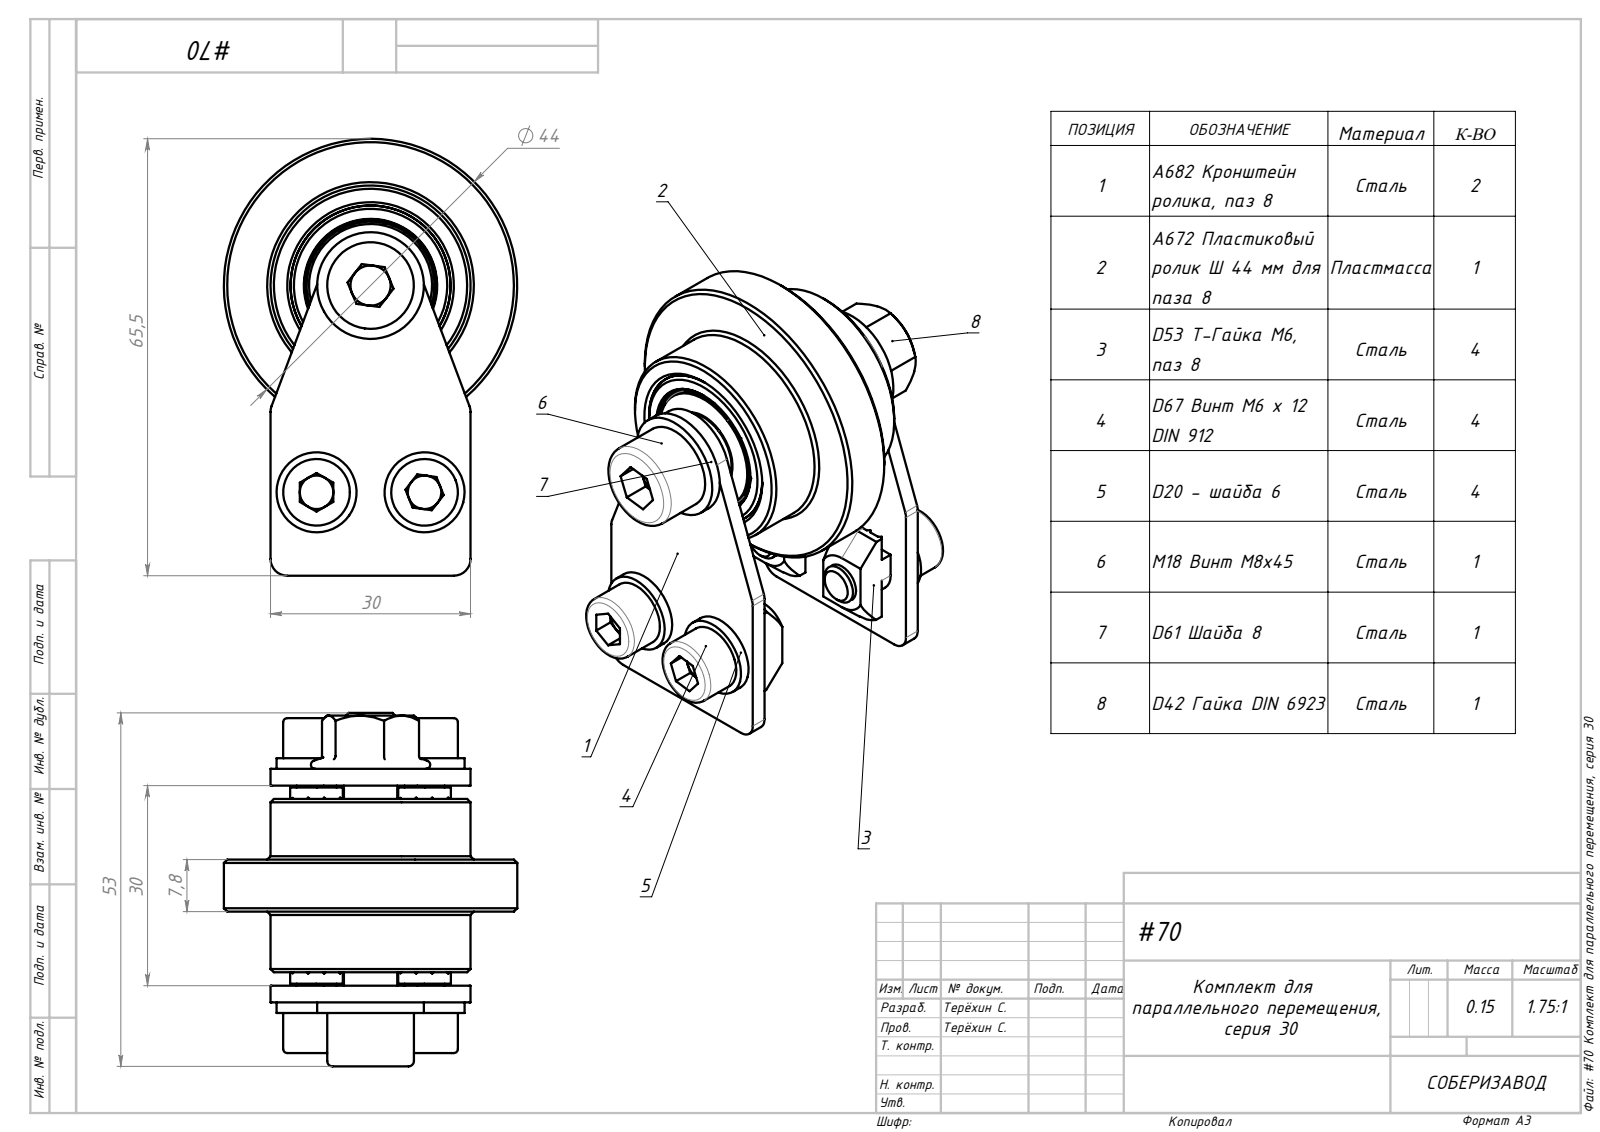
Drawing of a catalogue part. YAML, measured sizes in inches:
part_name: "Набор ролика, 30 серия; D61 Шайба 8_00; D53 Т-Гайка М6, паз 8_00; A682 Кронштейн ролика, паз 8_00 (+5 more)"
step_written_by: "SolidWorks 2022 (AUTOMOTIVE_DESIGN)"
units: inches
bodies: {solids: 24, faces: 655, planar: 397, cylindrical: 126, other: 132}
overall_size: [2.579, 2.087, 1.732]
volume: 2.181
surface_area: 42.48
round_holes:
  - {diameter: 0.197, count: 2}
  - {diameter: 0.244, count: 2}
  - {diameter: 0.252, count: 2}
  - {diameter: 0.268, count: 1}
  - {diameter: 0.315, count: 1}
  - {diameter: 0.323, count: 1}
  - {diameter: 0.331, count: 1}
  - {diameter: 0.48, count: 1}
  - {diameter: 0.787, count: 1}
  - {diameter: 0.945, count: 1}
round_bosses_or_shafts:
  - {diameter: 0.472, count: 3}
  - {diameter: 0.394, count: 2}
  - {diameter: 0.236, count: 2}
  - {diameter: 1.732, count: 1}
  - {diameter: 1.181, count: 1}
  - {diameter: 0.78, count: 1}
  - {diameter: 0.63, count: 1}
  - {diameter: 0.512, count: 1}
partial_cylinders:
  - {radius: 0.157, count: 8}
  - {radius: 0.098, count: 4}
  - {radius: 0.27, count: 4}
  - {radius: 0.295, count: 1}
face_to_face_distances: [0.098, 1.28, 1.378, 0.535, 0.843, 0.437, 0.744, 1.181, 0.307, 0.709]
hole_center_spacings: [1.261, 0.638]
